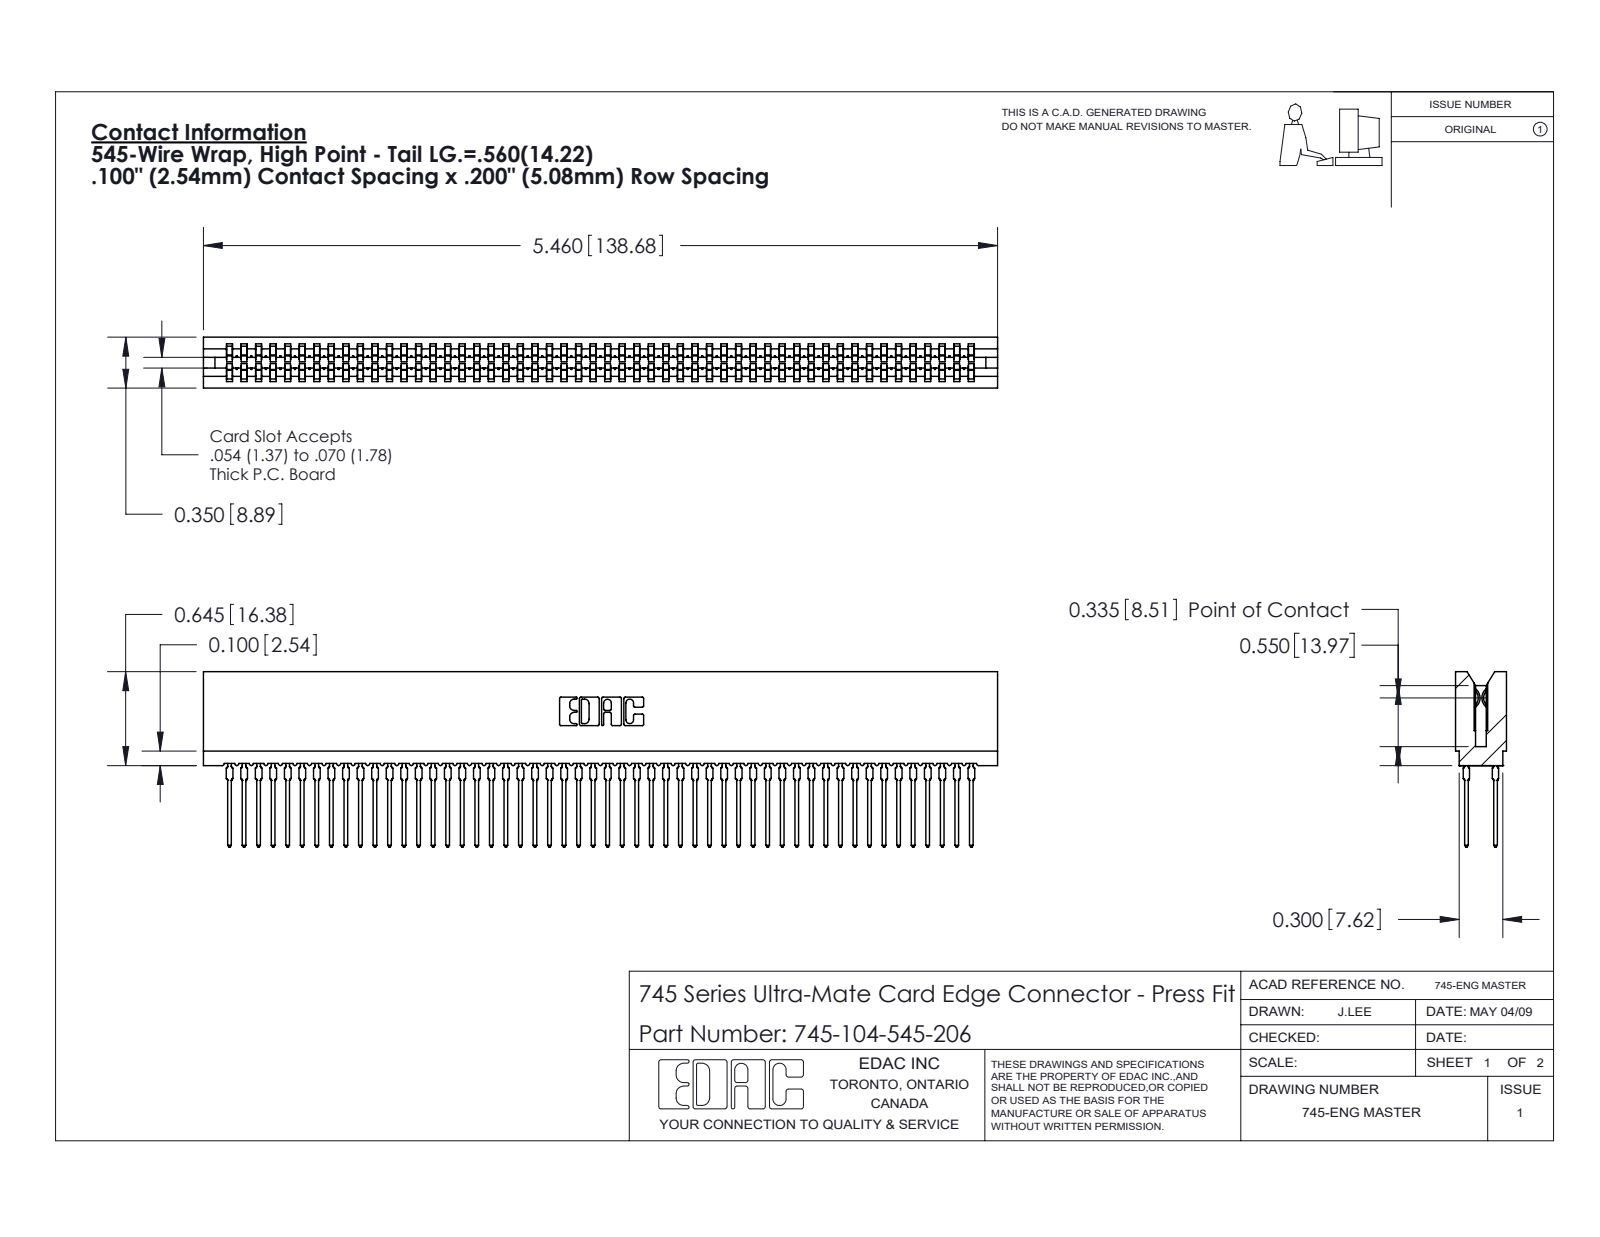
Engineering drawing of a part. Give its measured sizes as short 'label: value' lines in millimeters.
name: 745-292-001_545; 745 Part_Insulator Option - 06; 745-104-545-206
written by: SolidWorks 2020 (CONFIG_CONTROL_DESIGN)
unit: mm
bodies: 105 solids, 9404 faces (4840 planar, 1860 cylindrical, 2704 other)
size: 138.7 × 30.6 × 8.9
volume: 12 800 mm³; area: 27 810 mm²
rounds: 208× R0.5, 104× R0.4, 22× R0.3, 8× R0.1, 8× R0.3, 6× R0.2, 6× R0.8, 3× R0.7
face distances: 1.6, 7.3, 8.9, 5.1, 1.1, 7.7, 0.5, 6.2, 3.5, 5.4
